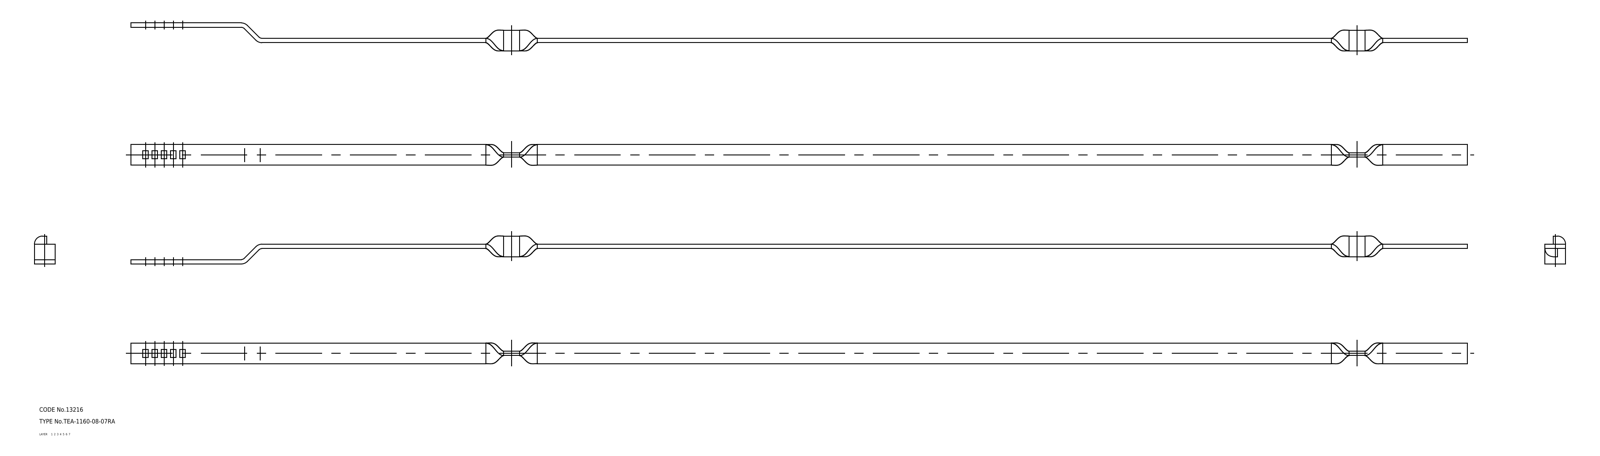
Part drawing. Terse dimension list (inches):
name: rod
written by: CADfix (AUTOMOTIVE_DESIGN)
unit: in
bodies: 1 solid, 66 faces (0 planar, 0 cylindrical, 66 other)
size: 35.787 × 0.75 × 0.572
volume: 2.32 in³; area: 48.6 in²
